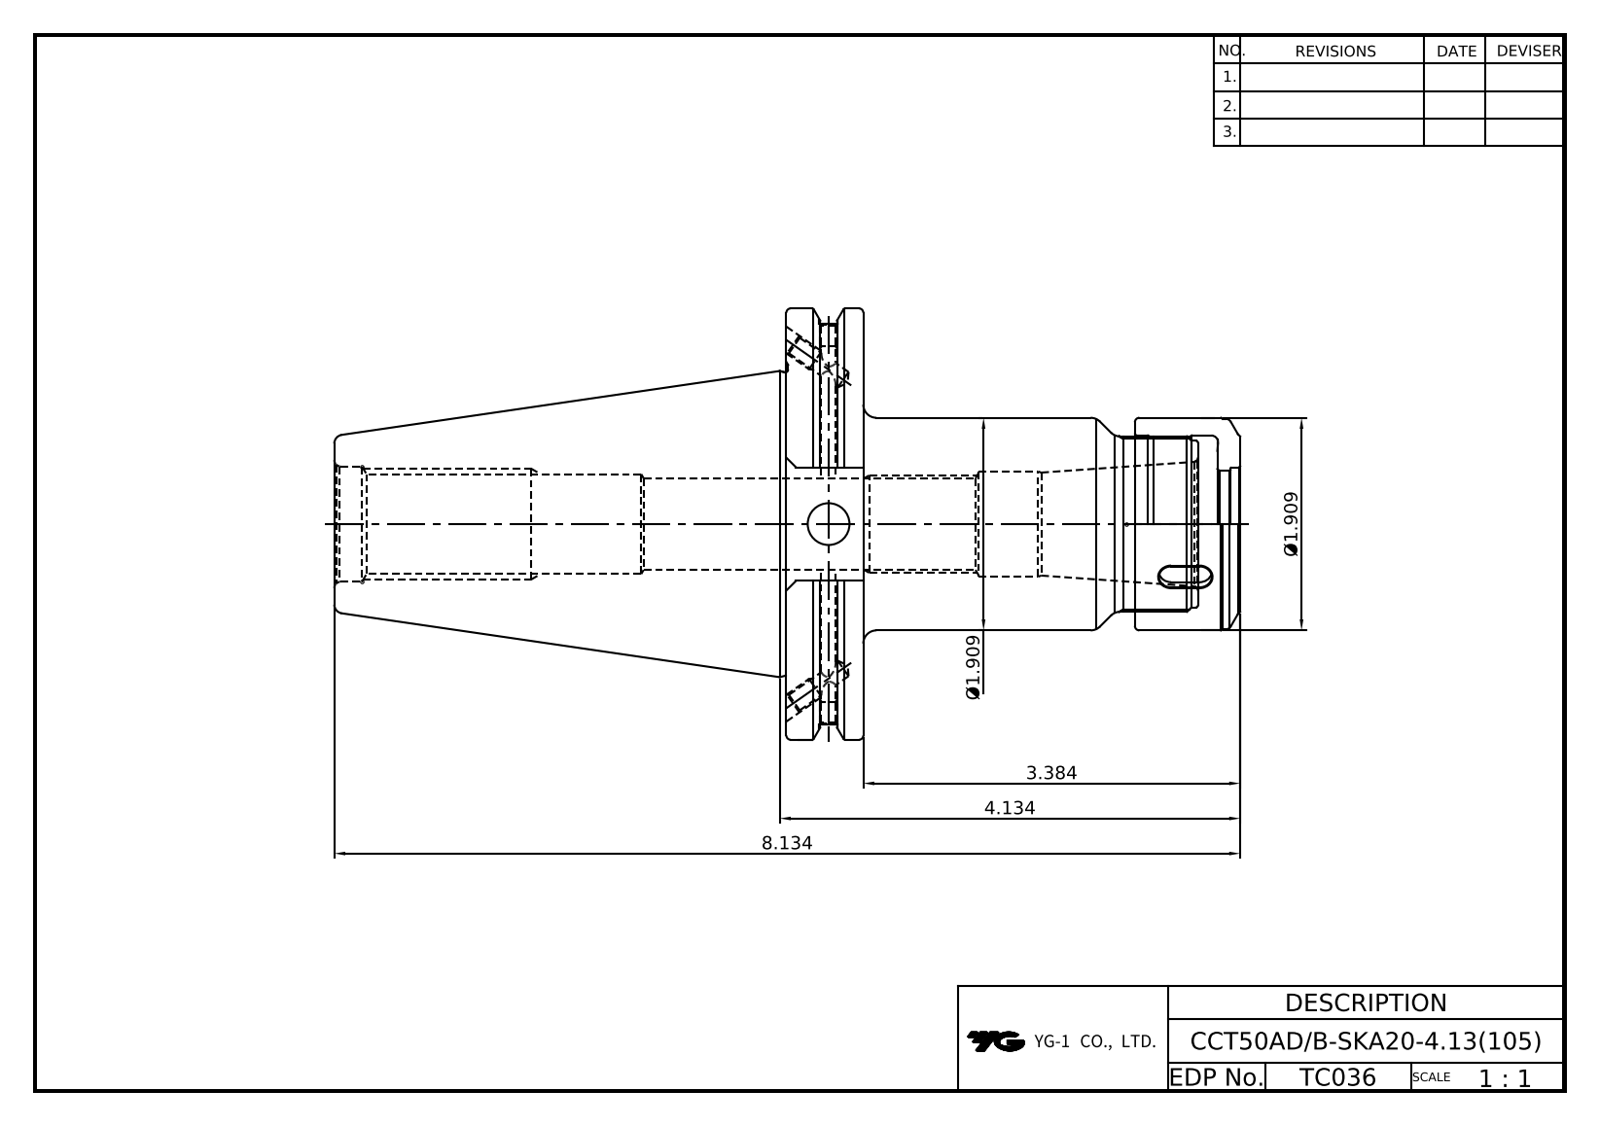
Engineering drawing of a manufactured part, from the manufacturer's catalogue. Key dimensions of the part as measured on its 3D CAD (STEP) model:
Part name (STEP PRODUCT): LO-CCT50ADB-SKA20-105; SKN20-NUT
STEP written by: Autodesk Inventor 2022 (AUTOMOTIVE_DESIGN)
Units: millimetres
Bodies: 2 solids, 170 faces (62 planar, 46 cylindrical, 62 other)
Overall size (bounding box): 206.6 × 98.42 × 94.69
Volume: 439 862 mm³ · Surface area: 69 132 mm²
Round holes (diameter × count): ⌀3.24 ×2, ⌀4.13 ×2, ⌀4.2 ×2, ⌀5 ×2, ⌀9.53 ×1, ⌀19.18 ×1, ⌀21.97 ×1, ⌀24 ×1, ⌀26.2 ×1, ⌀29.2 ×1, ⌀31 ×1, ⌀38.92 ×1
Round bosses / shafts (diameter × count): ⌀98.42 ×1, ⌀91.29 ×1, ⌀69.25 ×1, ⌀48.5 ×1, ⌀48.1 ×1, ⌀40 ×1, ⌀38 ×1
Main face-to-face distances: 17.55, 103.1, 103.5, 120.65, 206.6, 85.95, 197, 93.9, 76.35, 9.6
